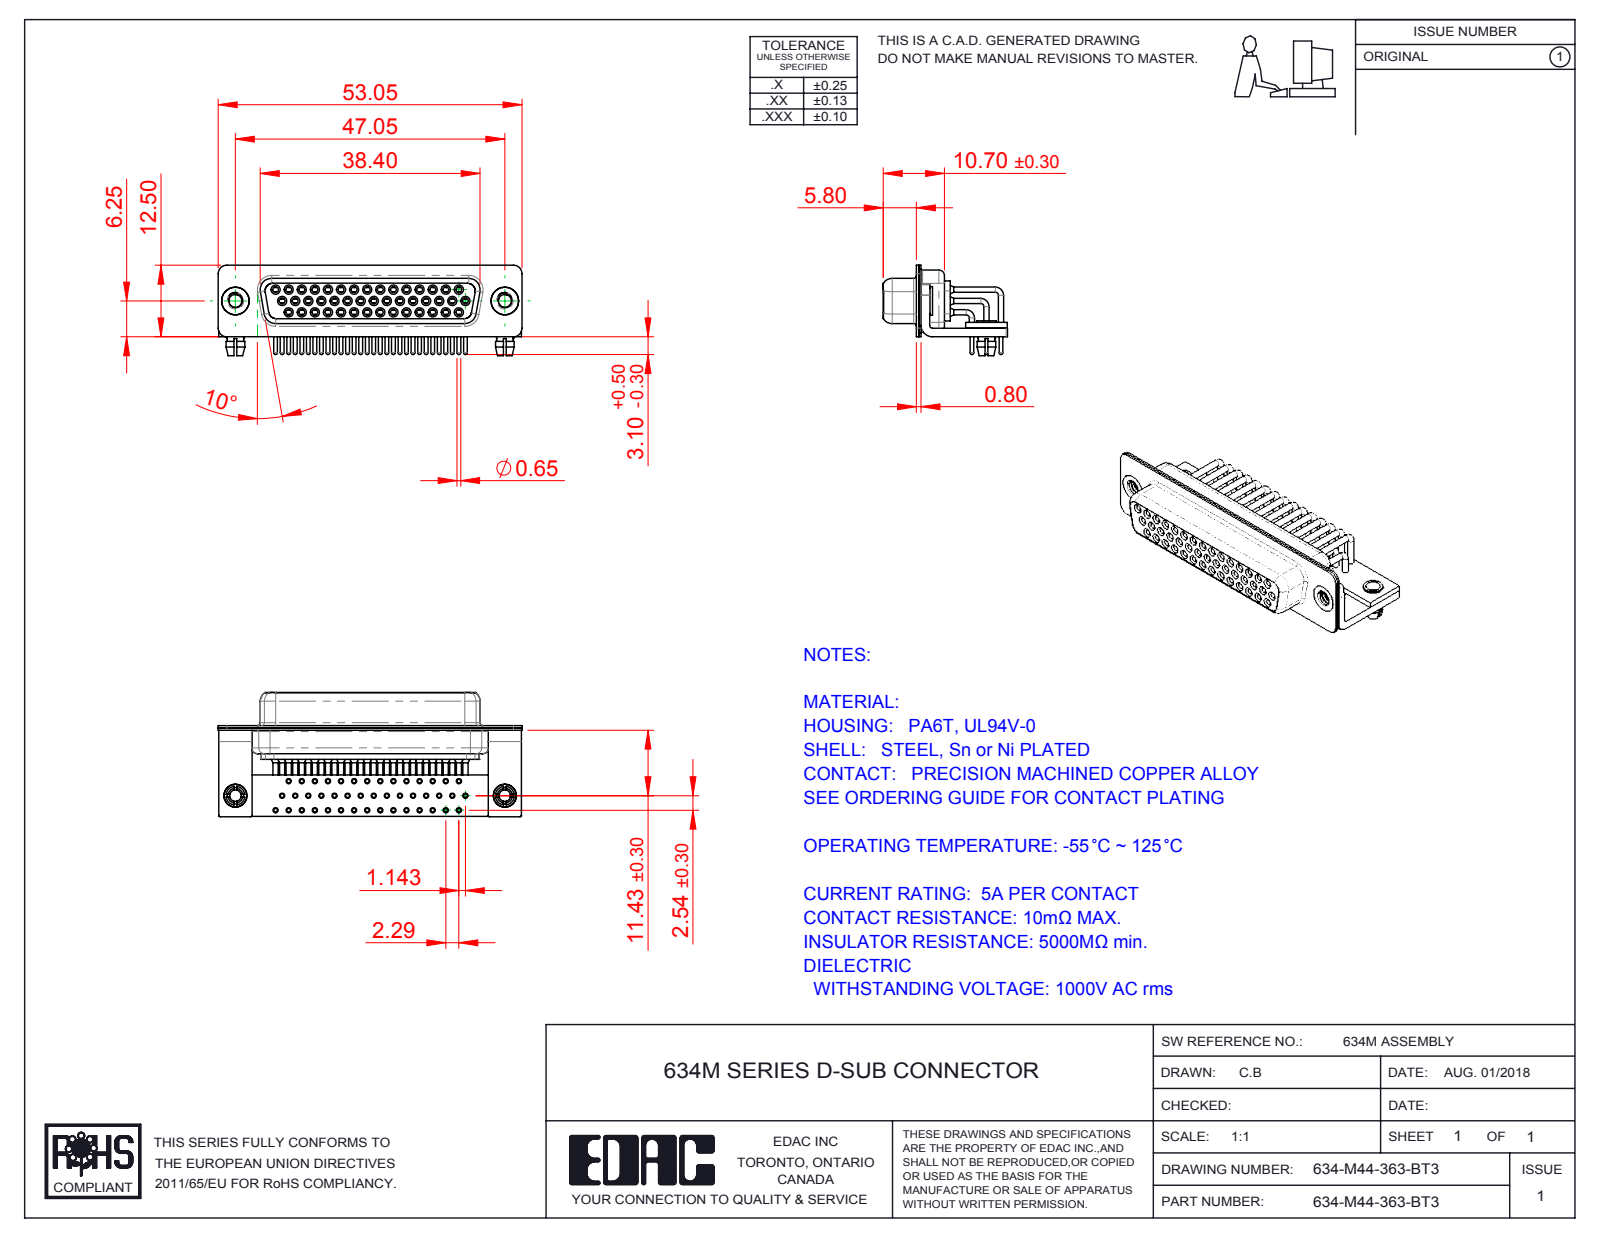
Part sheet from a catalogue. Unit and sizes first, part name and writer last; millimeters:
Units: millimetres
Overall size (bounding box): 53.05 × 21.7 × 15.8
Round holes (diameter × count): ⌀2 ×46, ⌀0.9 ×44, ⌀1 ×44, ⌀1.1 ×44, ⌀1.7 ×44, ⌀1.8 ×44, ⌀2.26 ×2, ⌀2.5 ×2, ⌀3.2 ×2, ⌀4 ×2, ⌀4.8 ×2
Round bosses / shafts (diameter × count): ⌀1.6 ×44, ⌀1.5 ×44, ⌀0.9 ×44, ⌀0.65 ×44, ⌀5 ×2, ⌀4.9 ×2, ⌀4 ×2, ⌀3.4 ×2
Partial cylindrical surfaces — rounded edges, fillets, slot ends (radius × count): R0.25 ×16, R1.5 ×16, R2 ×13, R1.35 ×8, R1.6 ×8, R0.5 ×5, R0.6 ×4, R0.65 ×4
Main face-to-face distances: 0.4, 2.3, 1, 1.9, 0.8, 9.35, 1.45, 8.95, 1.5, 0.85
Hole centre spacings: 2.28, 2.29, 4.57, 6.86, 11.43, 3.96, 8.24, 9.14
Volume: 4 503 mm³ · Surface area: 14 836 mm²
Bodies: 54 solids, 2841 faces (801 planar, 1291 cylindrical, 749 other)
Part name (STEP PRODUCT): 634M Shell Rear_44 Contacts; 634M Housing_44 Contacts; 634M Board Lock; 634M 4-40 Threaded Rivet_Stabilizer (+7 more)
STEP written by: SolidWorks 2016 (CONFIG_CONTROL_DESIGN)
